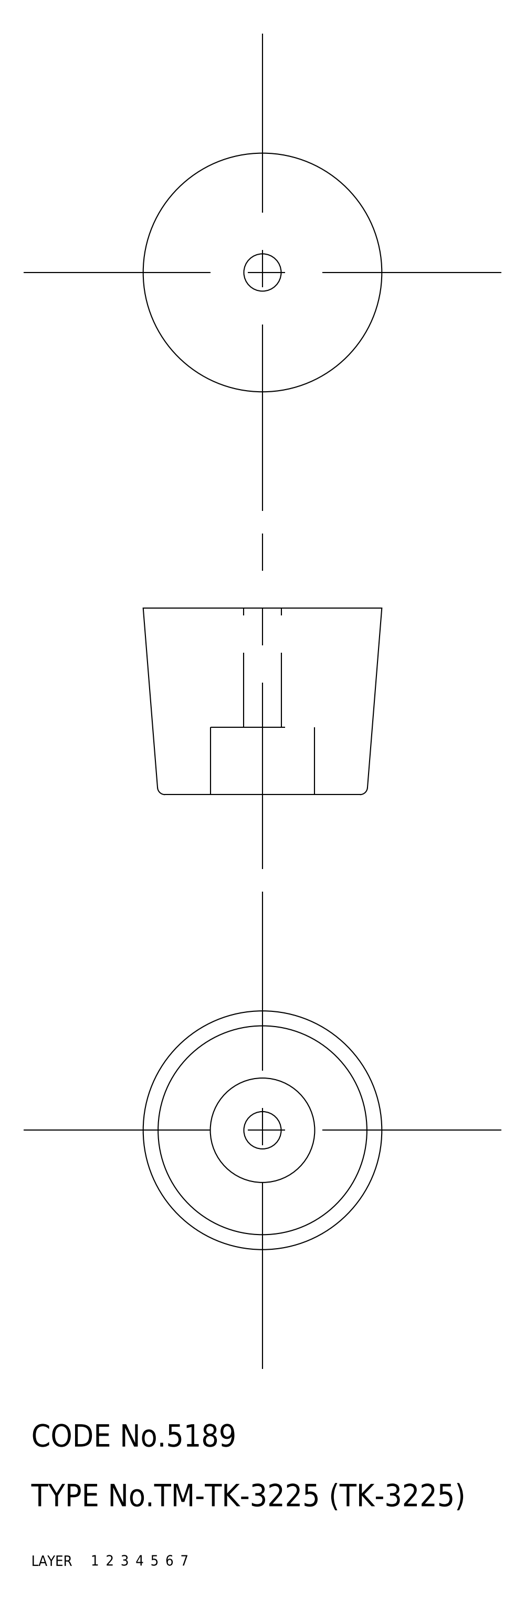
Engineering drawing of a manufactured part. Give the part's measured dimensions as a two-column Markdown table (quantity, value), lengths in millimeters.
| quantity | value |
| --- | --- |
| part name | washer; rubber foot; TK_3225_9741_36 |
| STEP written by | CADfix (AUTOMOTIVE_DESIGN) |
| units | millimeters |
| bodies | 2 solids, 20 faces (0 planar, 0 cylindrical, 20 other) |
| overall size | 32 × 32 × 25 |
| volume | 16 018 mm³ |
| surface area | 4 900 mm² |
